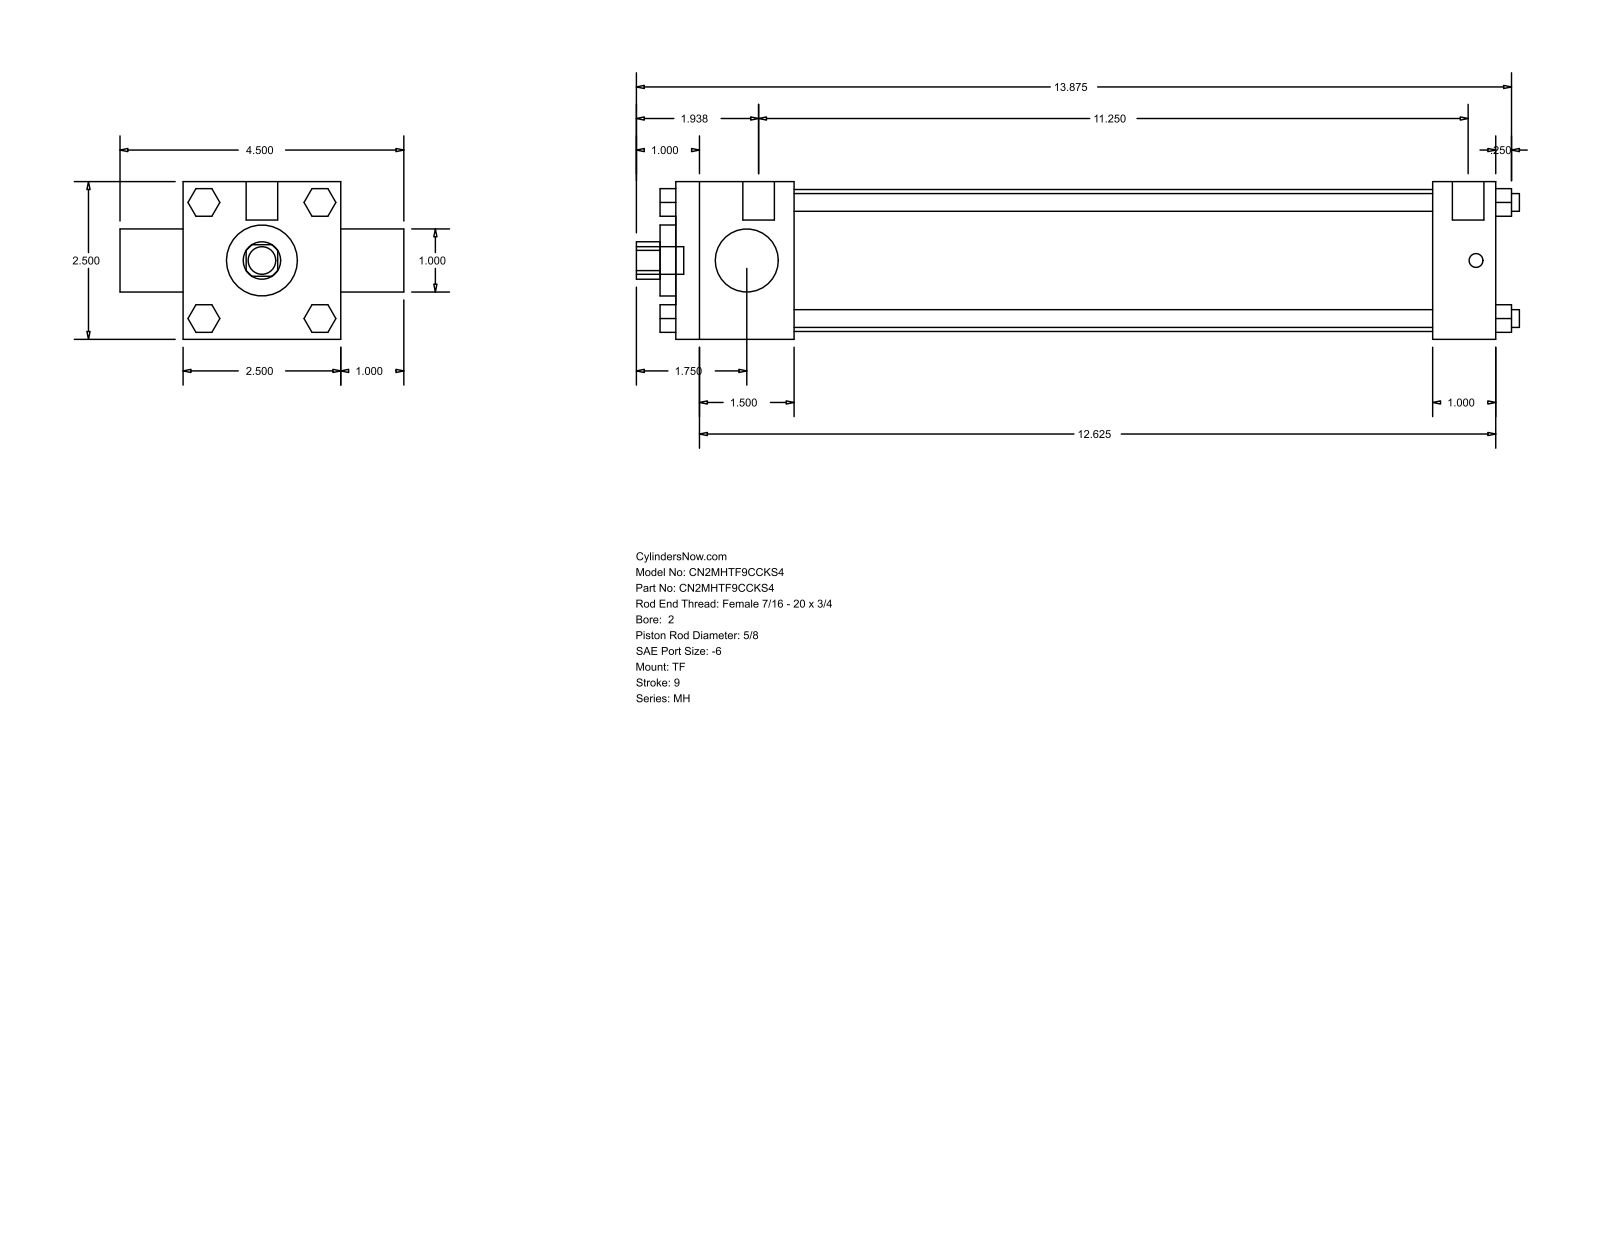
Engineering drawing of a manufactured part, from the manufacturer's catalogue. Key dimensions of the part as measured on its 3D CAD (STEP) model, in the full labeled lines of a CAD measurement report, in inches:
Part name (STEP PRODUCT): MH_TF__0200_0.625
STEP written by: GSSL Pune (CONFIG_CONTROL_DESIGN)
Units: inches
Bodies: 0 solids, 120 faces (92 planar, 28 cylindrical, 0 other)
Overall size (bounding box): 14 × 4.5 × 2.5
Round holes (diameter × count): ⌀0.625 ×1, ⌀1 ×1, ⌀1.125 ×1, ⌀2.25 ×1
Round bosses / shafts (diameter × count): ⌀0.281 ×4, ⌀0.219 ×3, ⌀0.5 ×2, ⌀0.437 ×1
Partial cylindrical surfaces — rounded edges, fillets, slot ends (radius × count): R0.297 ×1
Main face-to-face distances: 2.5, 13, 1.875, 12, 10.125, 11.125, 1, 1, 3.5, 0.25
